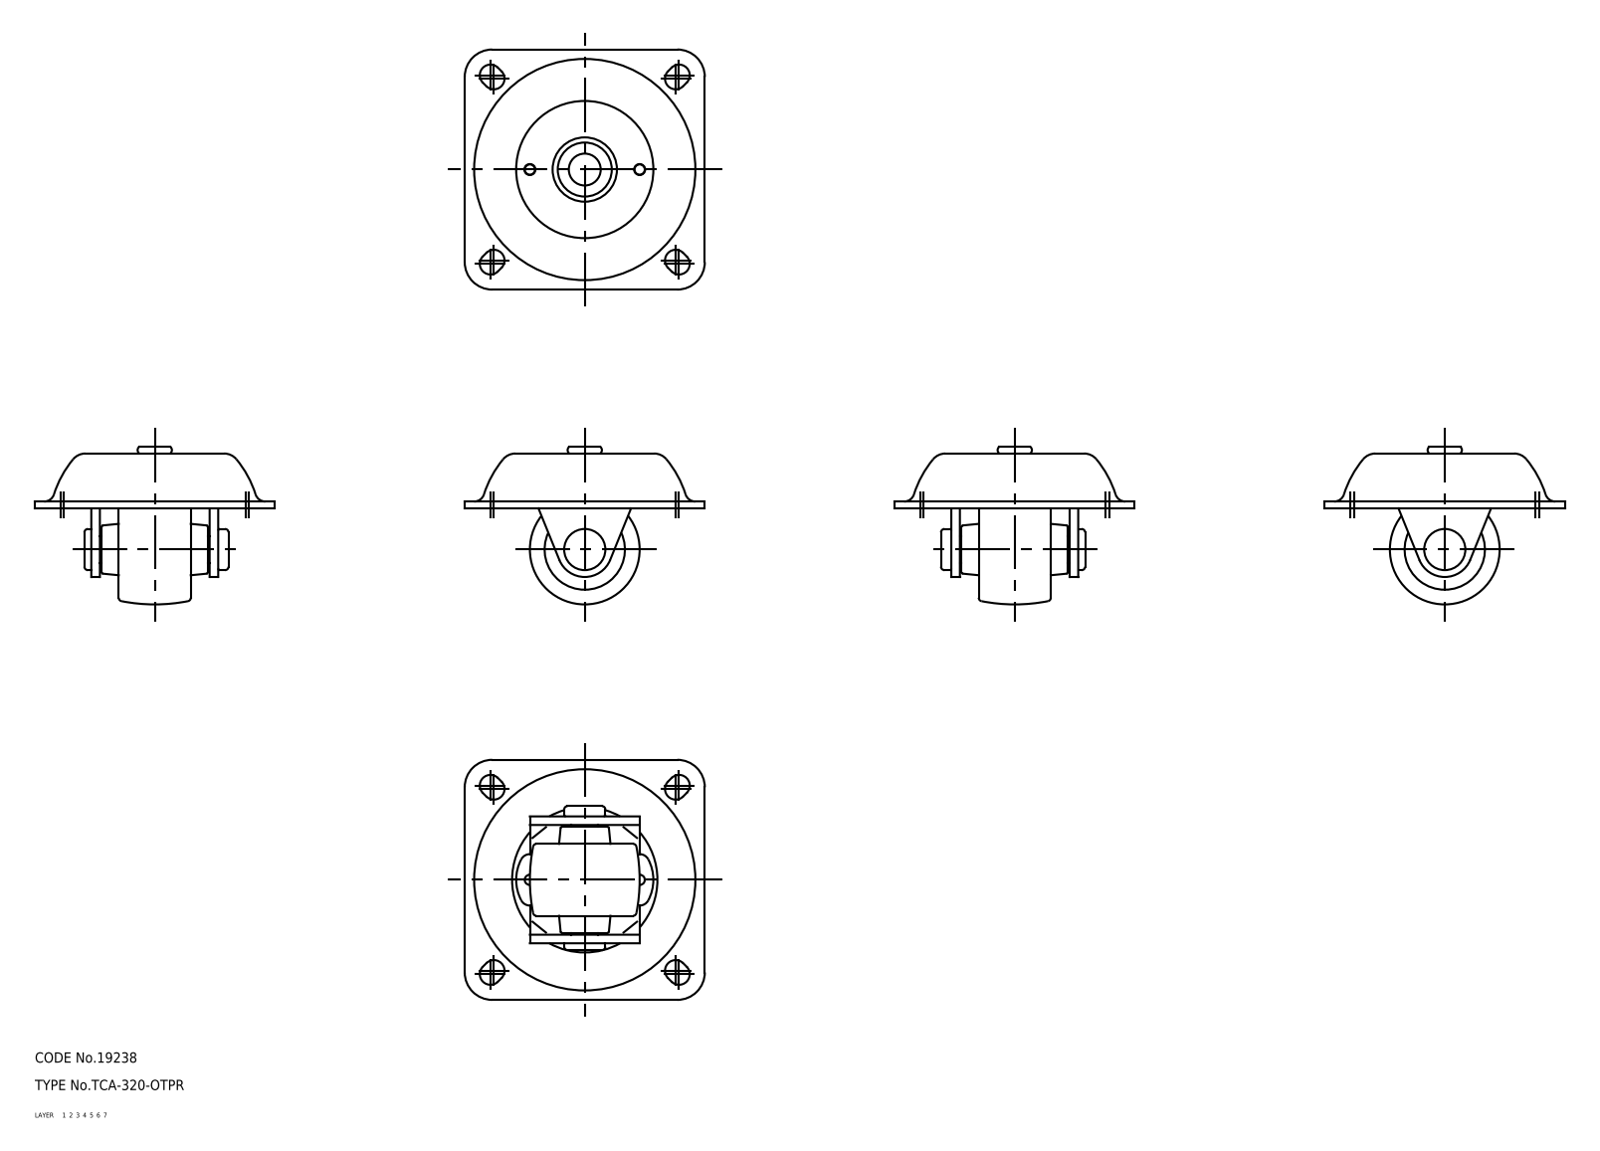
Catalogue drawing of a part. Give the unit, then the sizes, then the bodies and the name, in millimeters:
Units: millimetres
Overall size (bounding box): 70 × 70 × 46
Volume: 36 519 mm³ · Surface area: 25 613 mm²
Bodies: 5 solids, 184 faces (0 planar, 0 cylindrical, 184 other)
Part name (STEP PRODUCT): axle; mounting plate; wheel; main shaft (+1 more)
STEP written by: CADfix (AUTOMOTIVE_DESIGN)
